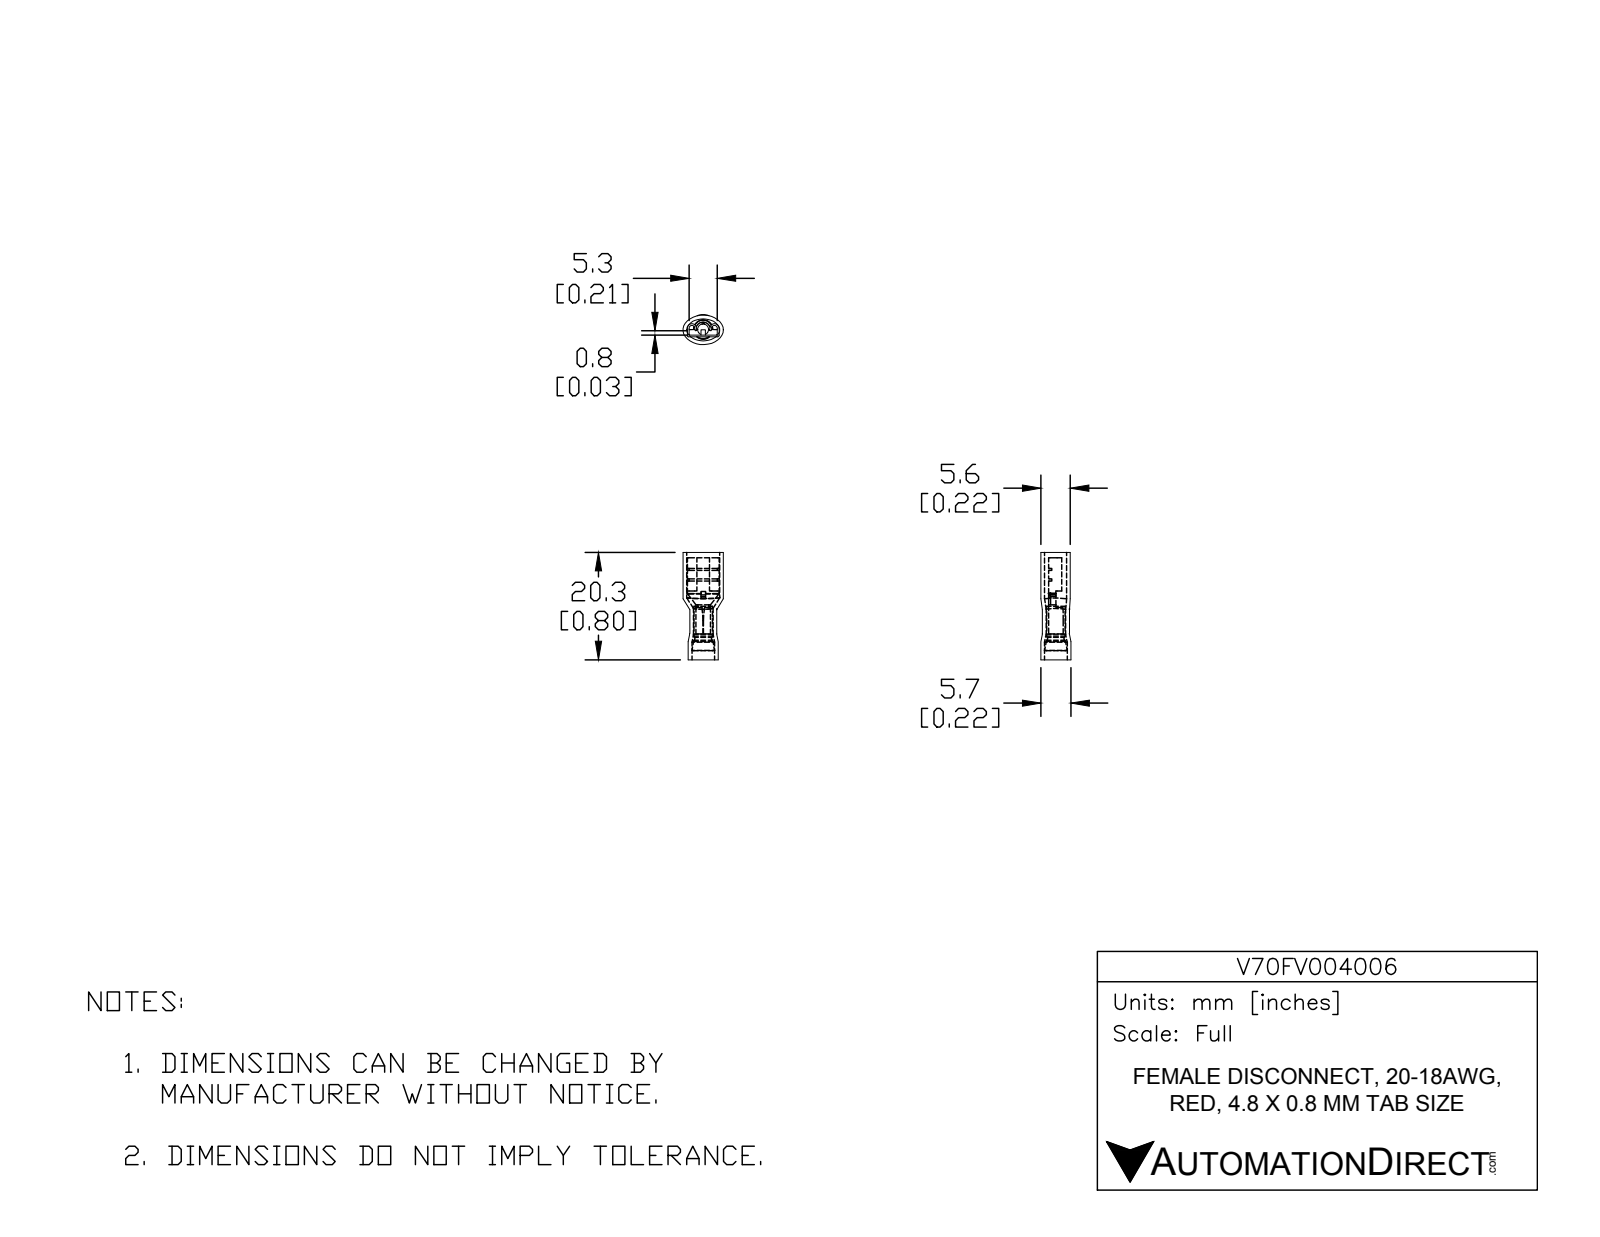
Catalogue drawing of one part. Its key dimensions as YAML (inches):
part_name: "V70FV004006"
step_written_by: "SolidWorks 2017 (AUTOMOTIVE_DESIGN)"
units: inches
bodies: {solids: 3, faces: 127, planar: 51, cylindrical: 36, other: 40}
overall_size: [0.8, 0.3, 0.224]
volume: 0.019
surface_area: 1.84
round_holes:
  - {diameter: 0.081, count: 1}
  - {diameter: 0.109, count: 1}
  - {diameter: 0.146, count: 1}
  - {diameter: 0.169, count: 1}
round_bosses_or_shafts:
  - {diameter: 0.224, count: 1}
  - {diameter: 0.201, count: 1}
  - {diameter: 0.137, count: 1}
  - {diameter: 0.108, count: 1}
partial_cylinders:
  - {radius: 0.005, count: 2}
  - {radius: 0.01, count: 2}
  - {radius: 0.02, count: 2}
  - {radius: 0.034, count: 2}
  - {radius: 0.619, count: 2}
  - {radius: 0.011, count: 1}
  - {radius: 0.025, count: 1}
face_to_face_distances: [0.014, 0.222, 0.8, 0.236, 0.209, 0.079, 0.094, 0.041, 0.76, 0.016]
